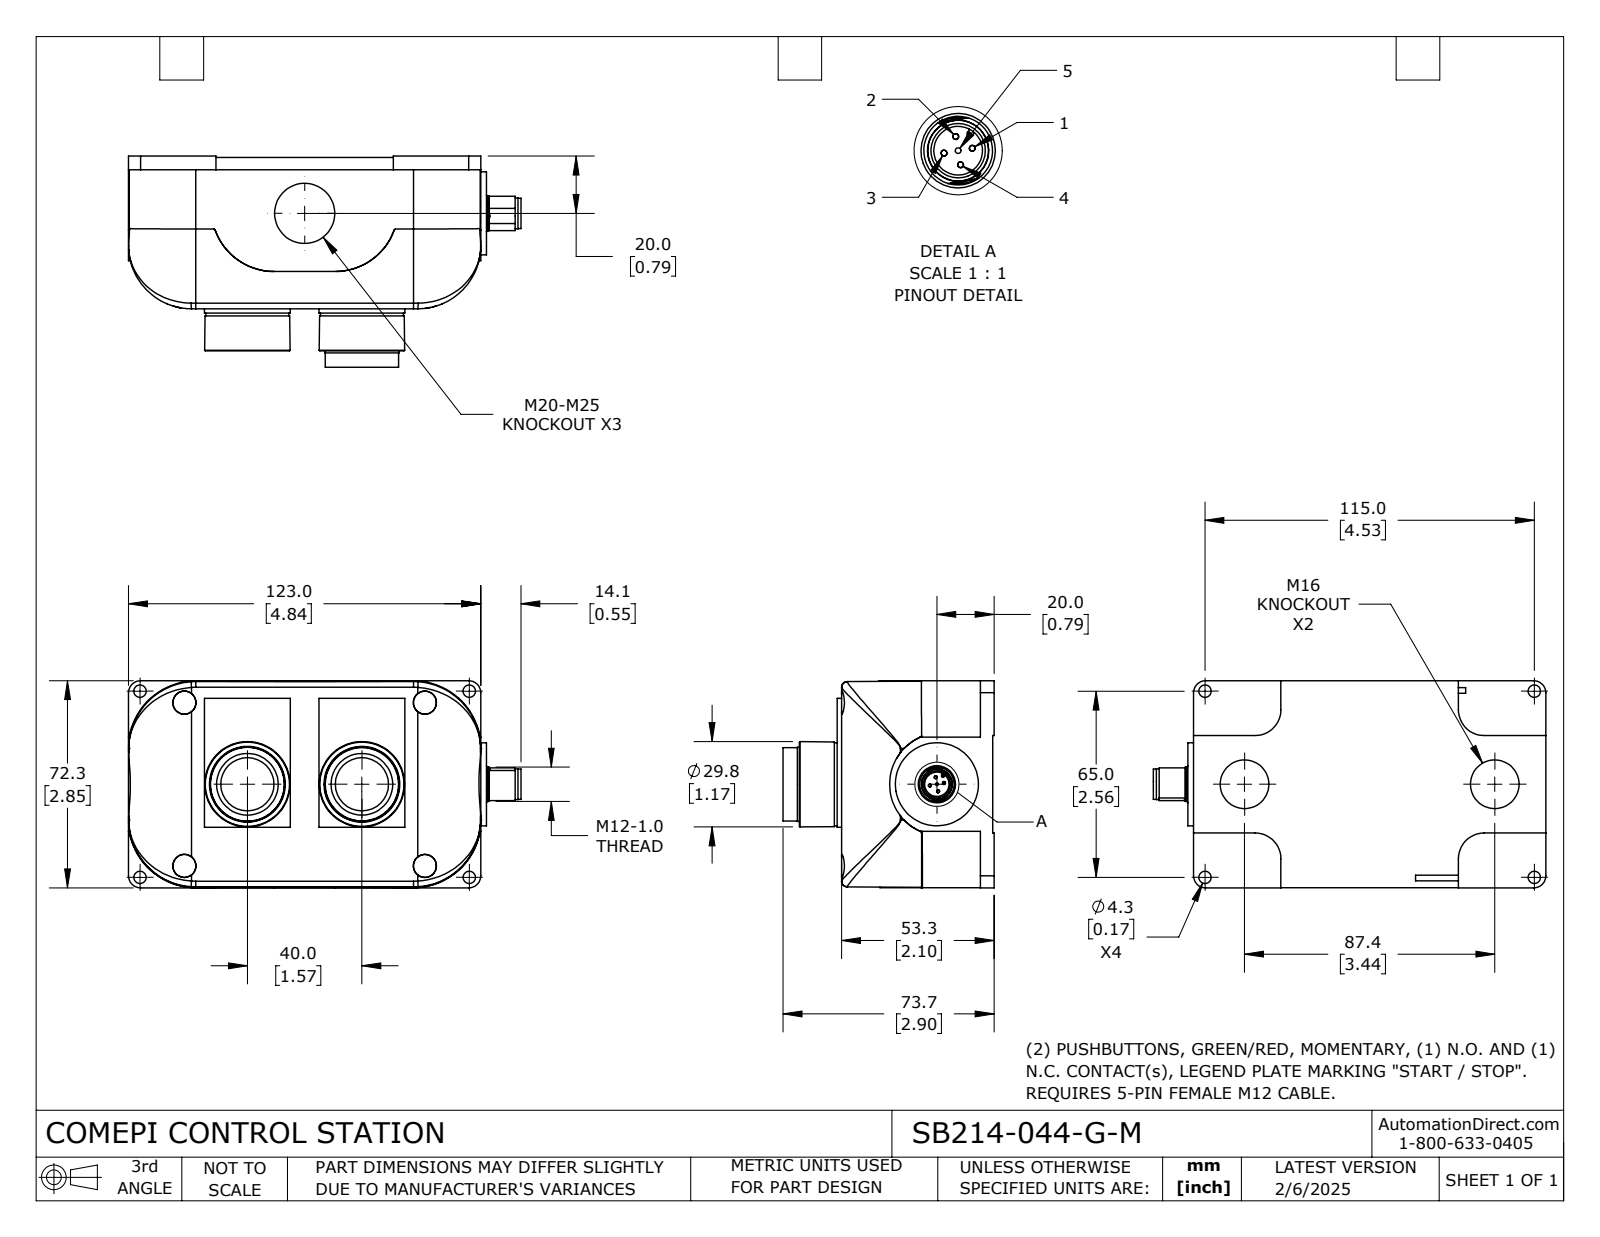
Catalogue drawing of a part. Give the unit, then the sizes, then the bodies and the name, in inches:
Units: inches
Overall size (bounding box): 5.396 × 2.902 × 2.846
Round holes (diameter × count): ⌀0.04 ×4, ⌀0.067 ×4, ⌀0.087 ×4, ⌀0.169 ×4, ⌀0.531 ×2, ⌀0.669 ×2, ⌀0.827 ×2, ⌀0.854 ×2, ⌀0.886 ×2, ⌀0.335 ×1
Round bosses / shafts (diameter × count): ⌀0.039 ×5, ⌀0.085 ×4, ⌀0.065 ×4, ⌀1.142 ×3, ⌀0.748 ×2, ⌀0.63 ×2, ⌀0.614 ×2, ⌀0.024 ×2
Partial cylindrical surfaces — rounded edges, fillets, slot ends (radius × count): R0.02 ×5, R0.01 ×4, R0.035 ×4, R0.079 ×4, R0.157 ×4, R0.354 ×4, R0.38 ×4, R0.866 ×4
Main face-to-face distances: 2.079, 0.098, 1.98, 0.976, 0.878, 1.102, 0.118, 2.157, 2.138, 2.039
Hole centre spacings: 1.39, 1.954, 3.309, 4.185, 0.098, 0.139, 0.139, 0.933
Volume: 16.9 in³ · Surface area: 137.4 in²
Bodies: 16 solids, 692 faces (274 planar, 243 cylindrical, 175 other)
Part name (STEP PRODUCT): SB214-044-G-M
STEP written by: SolidWorks 2024 (CONFIG_CONTROL_DESIGN)
